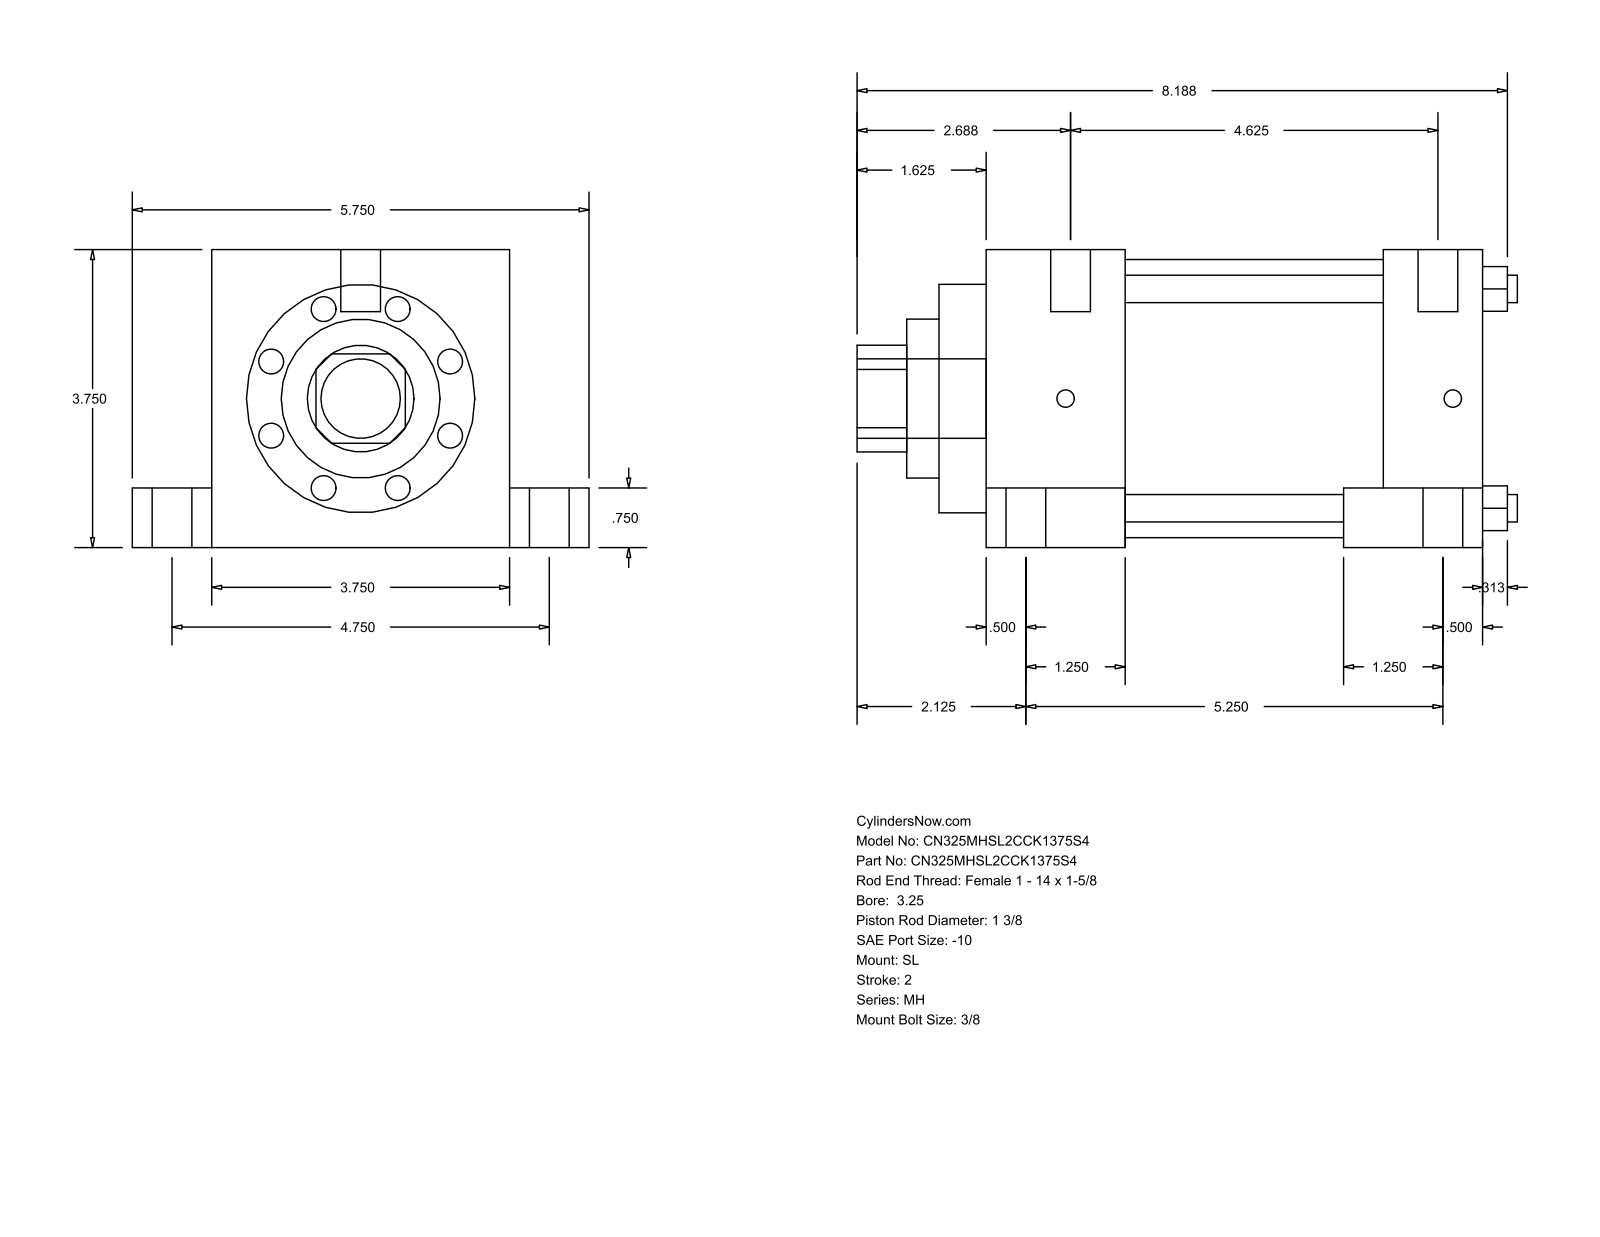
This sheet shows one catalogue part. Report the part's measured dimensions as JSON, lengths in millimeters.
{"part_name": "MH_SL__0325_1.375", "step_written_by": "GSSL Pune (CONFIG_CONTROL_DESIGN)", "units": "millimeters", "bodies": {"solids": 0, "faces": 110, "planar": 77, "cylindrical": 33, "other": 0}, "overall_size": [211.14, 146.05, 95.25], "round_holes": [[8.76, 4], [34.92, 1], [50.8, 1], [73.03, 1], [88.9, 1]], "round_bosses_or_shafts": [[12.7, 6], [19.05, 4], [5.56, 4], [25.4, 1]], "partial_cylinders_radius": [[17.06, 1]], "face_to_face_distances": [95.24, 158.76, 44.45, 114.31, 25.41, 120.65, 19.05, 76.19, 127.01, 82.56], "hole_center_spacings": [49.57, 70.1, 99.14]}
